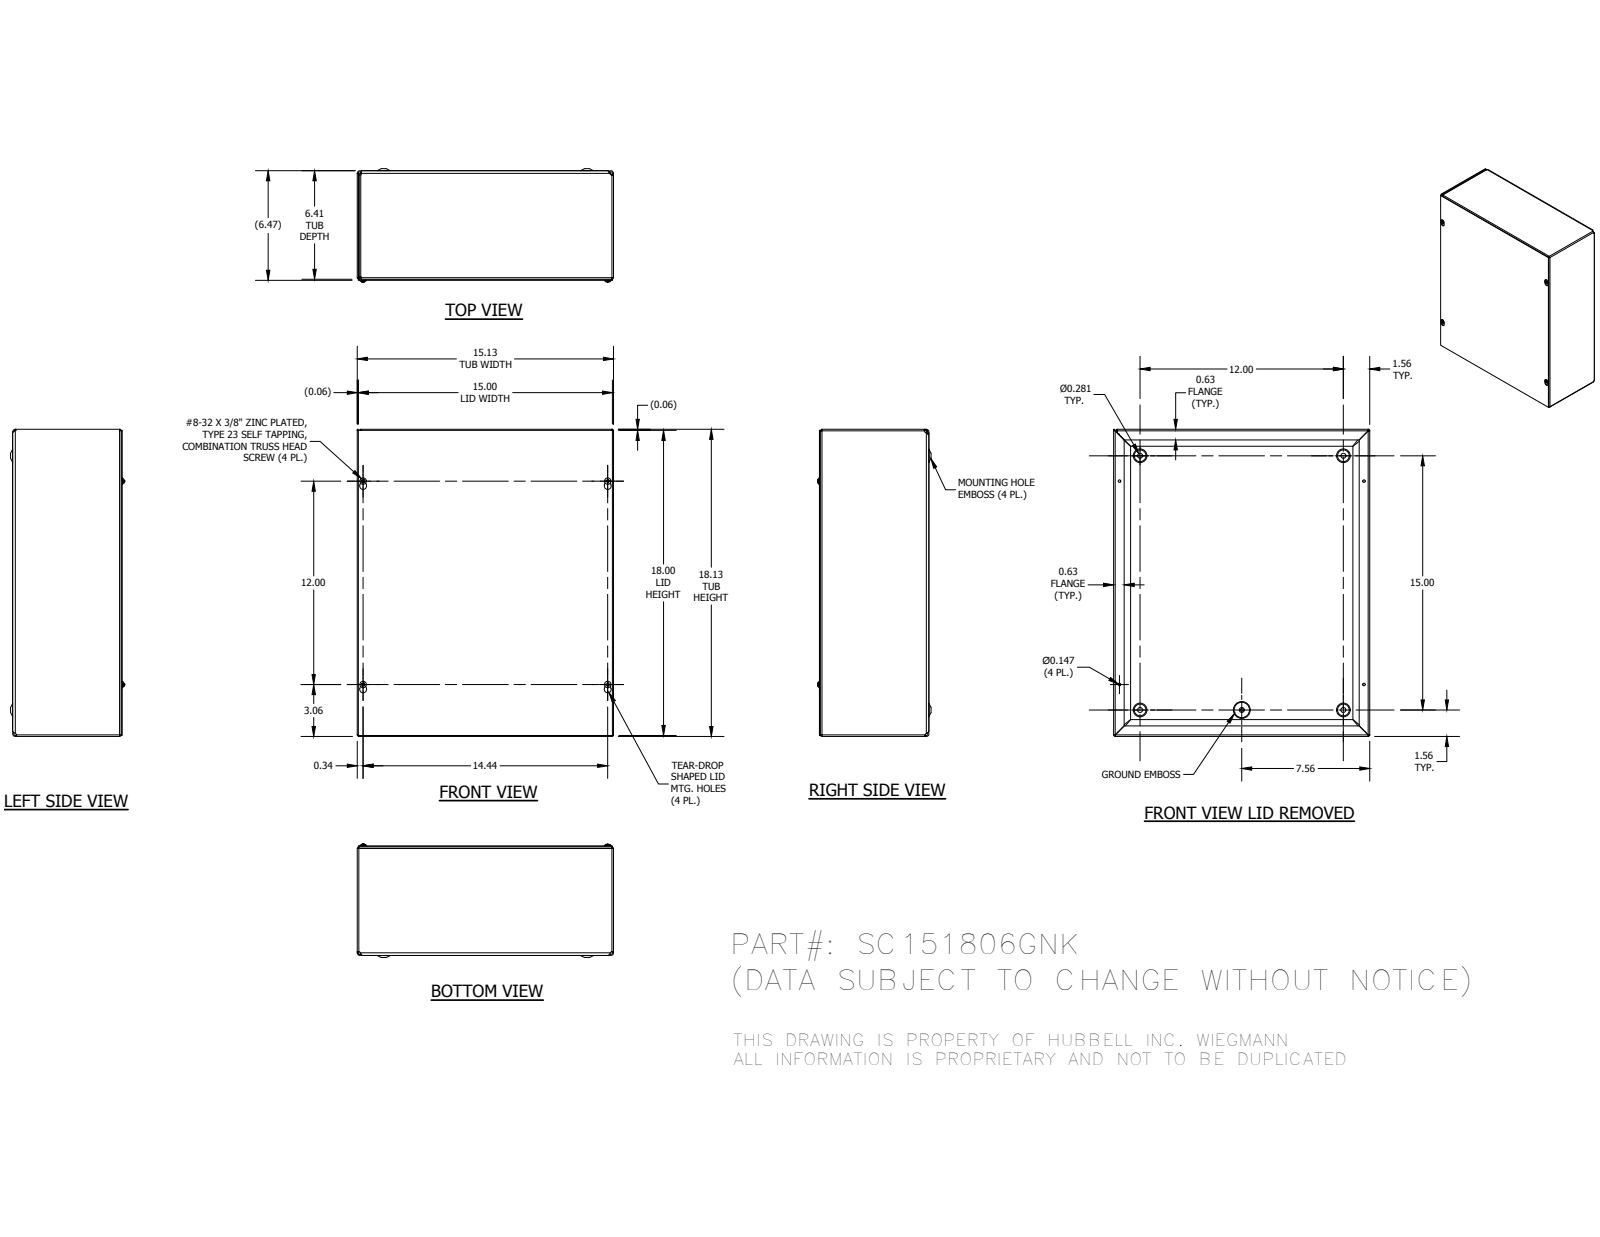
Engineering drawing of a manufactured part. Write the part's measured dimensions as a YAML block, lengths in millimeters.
part_name: "SC1518GNKBKP; SC151806GNKWRA; SC1518GNKLID; 34056 (+1 more)"
step_written_by: "Autodesk Inventor 2014 (AUTOMOTIVE_DESIGN)"
units: millimeters
bodies: {solids: 7, faces: 358, planar: 133, cylindrical: 73, other: 152}
overall_size: [460.38, 384.18, 170]
volume: 1064000
surface_area: 1361000
round_holes:
  - {diameter: 3.73, count: 4}
  - {diameter: 7.62, count: 4}
  - {diameter: 4.19, count: 1}
round_bosses_or_shafts:
  - {diameter: 9.75, count: 4}
  - {diameter: 4.17, count: 4}
  - {diameter: 5.8, count: 1}
partial_cylinders:
  - {radius: 0.79, count: 8}
  - {radius: 2.37, count: 8}
  - {radius: 1.4, count: 4}
  - {radius: 1.57, count: 4}
  - {radius: 2.38, count: 4}
  - {radius: 2.97, count: 4}
  - {radius: 3.15, count: 4}
  - {radius: 3.17, count: 4}
face_to_face_distances: [1.57, 161.12, 162.69, 1.59, 162.71, 164.28, 1.58, 382.6, 381.03, 384.18]
hole_center_spacings: [304.8, 152.4, 337.91, 344.27, 344.31, 366.71, 381, 410.35]
